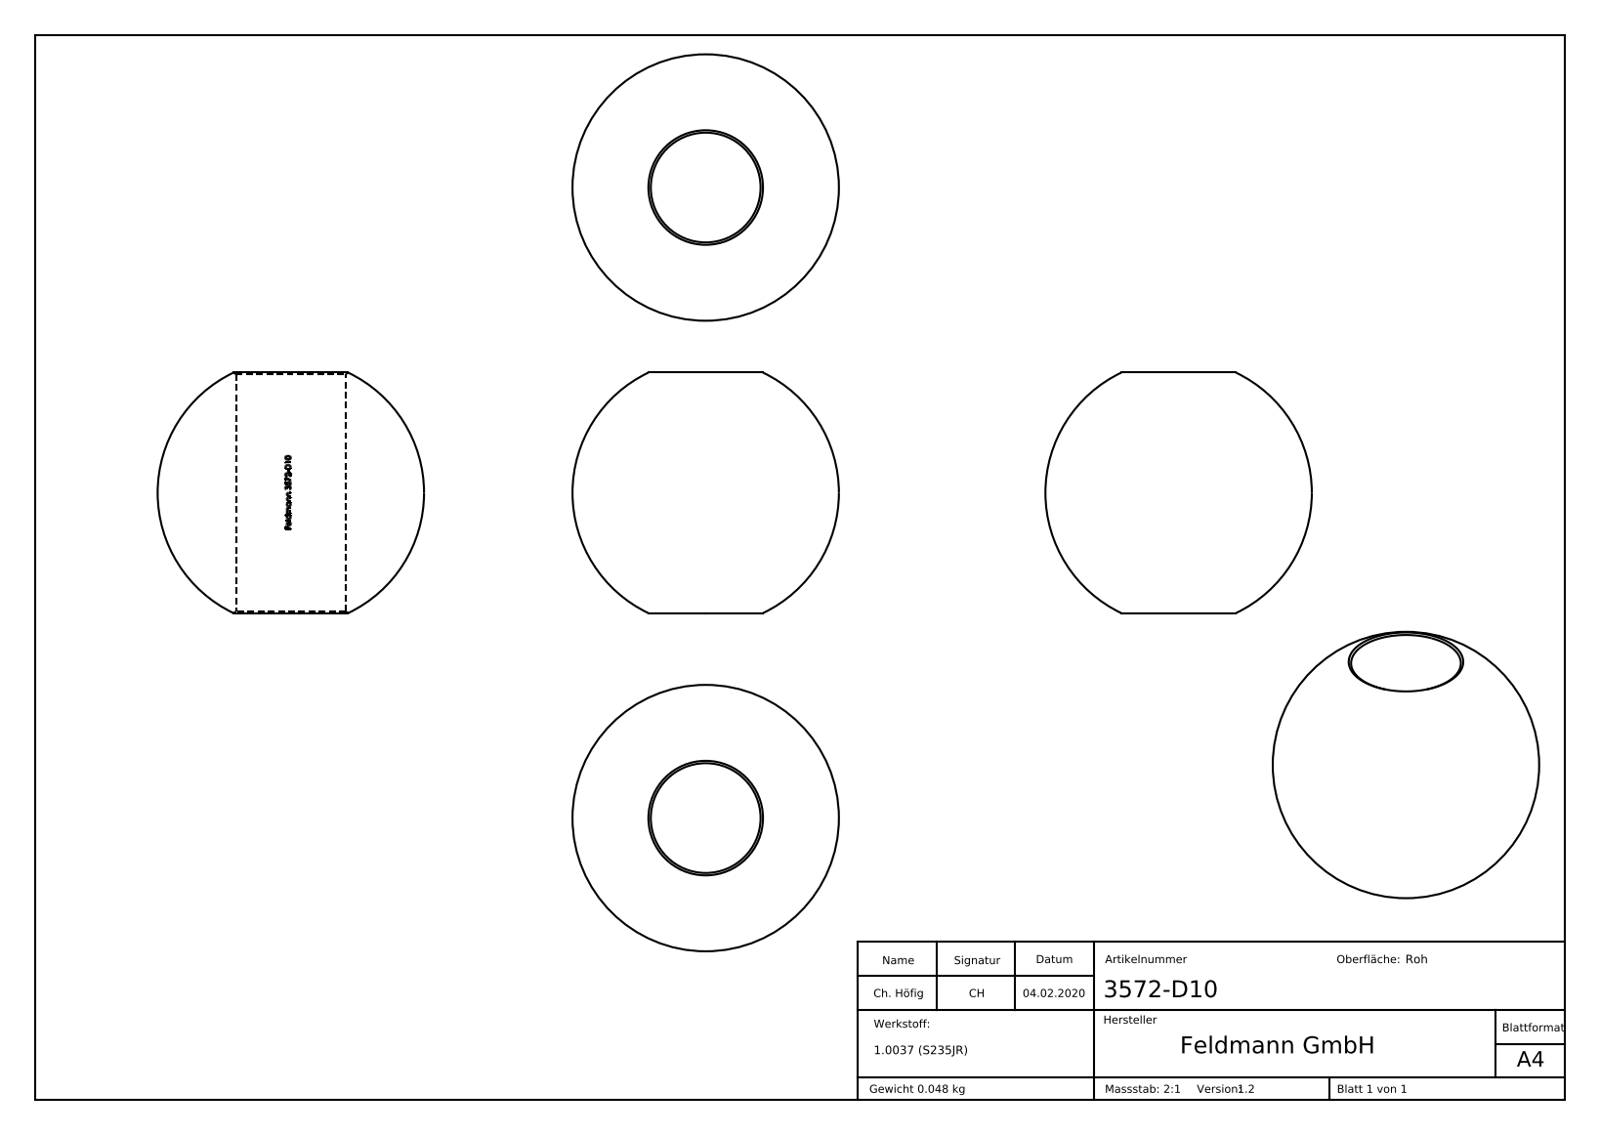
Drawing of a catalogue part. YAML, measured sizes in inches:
part_name: "3572-D10"
step_written_by: "SolidWorks 2015 (CONFIG_CONTROL_DESIGN)"
units: inches
bodies: {solids: 1, faces: 208, planar: 91, cylindrical: 22, other: 95}
overall_size: [0.984, 0.984, 0.889]
volume: 0.378
surface_area: 3.898
round_holes:
  - {diameter: 0.406, count: 1}
partial_cylinders:
  - {radius: 0.207, count: 1}
face_to_face_distances: [0.19, 0.021, 0.02, 0.024, 0.026, 0.1, 0.122, 0.046, 0.028, 0.032]
